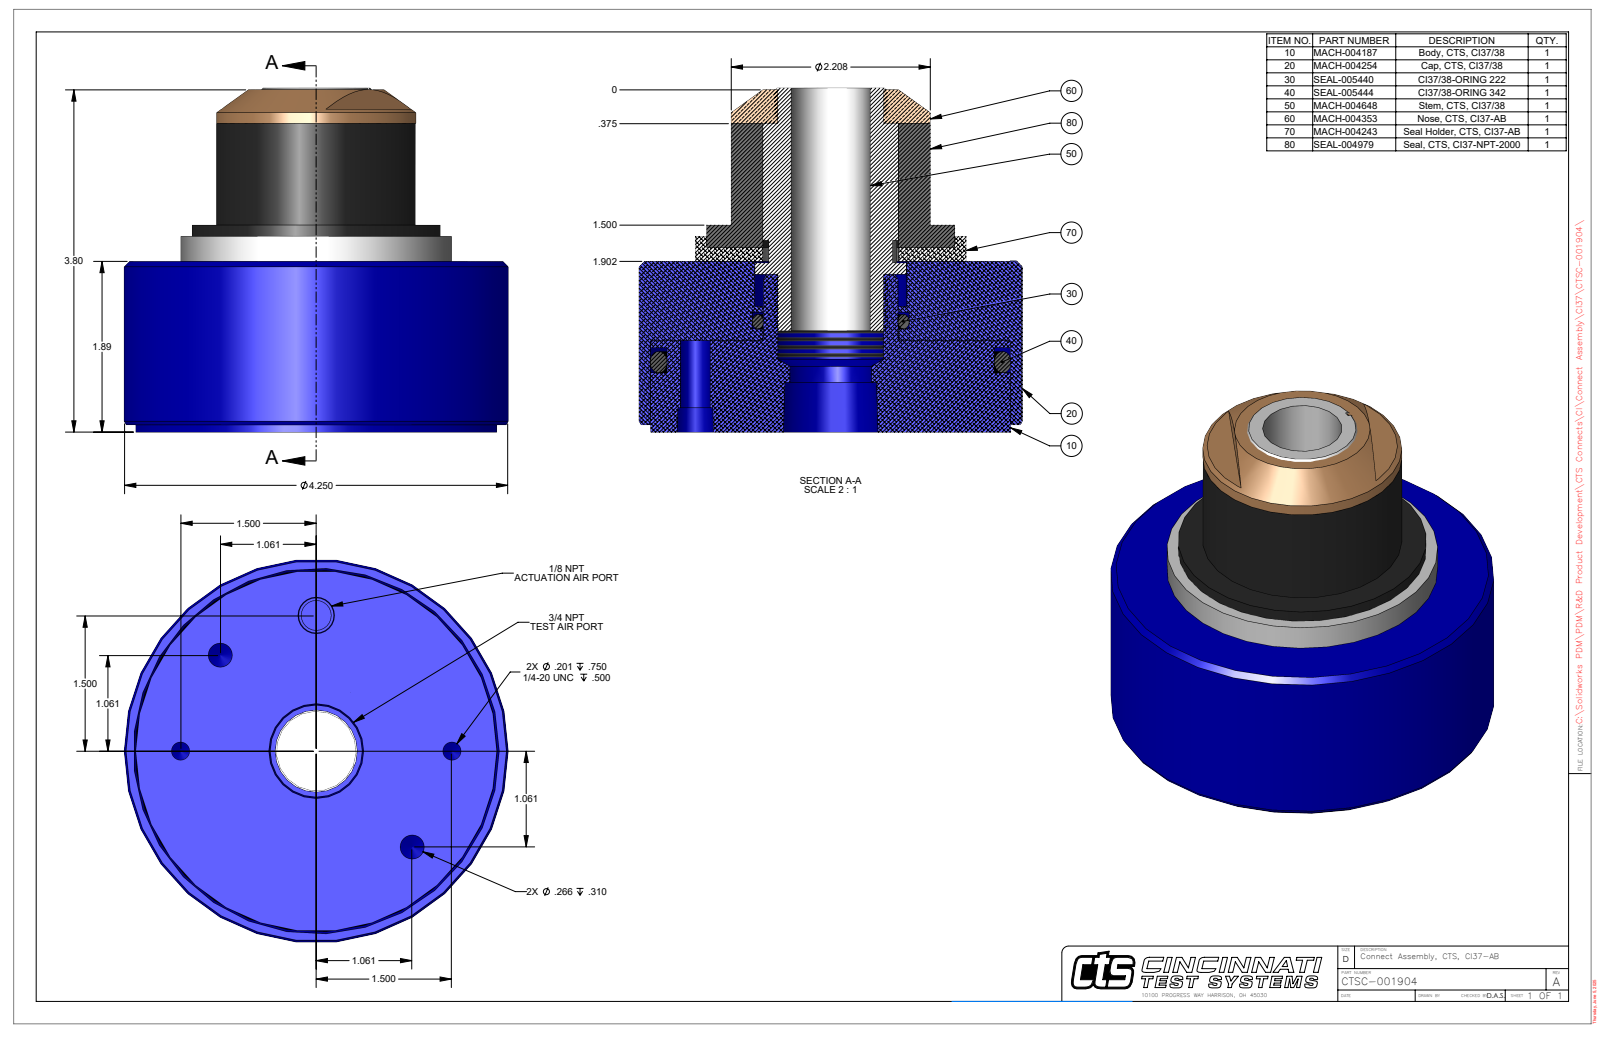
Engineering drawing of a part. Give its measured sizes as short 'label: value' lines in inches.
name: CTSC-001904
written by: SolidWorks 2023 (AUTOMOTIVE_DESIGN)
unit: in
bodies: 1 solid, 86 faces (30 planar, 35 cylindrical, 21 other)
size: 4.25 × 4.25 × 3.813
volume: 32.19 in³; area: 104.7 in²
holes: 2× ⌀0.201, 2× ⌀0.266, 1× ⌀0.332, 1× ⌀0.88, 1× ⌀1.504, 1× ⌀1.51, 1× ⌀1.688, 1× ⌀4
bosses: 1× ⌀4.25, 1× ⌀3.992, 1× ⌀3, 1× ⌀2.75, 1× ⌀2.208, 1× ⌀1.674, 1× ⌀1.5
rounds: 1× R0.586
face distances: 1.893, 2.295, 0.402, 2.17, 0.277, 0.125, 0.083, 1.81, 2.087, 2.212
hole spacings: 1.5, 1.148, 2.772, 2.121, 3
